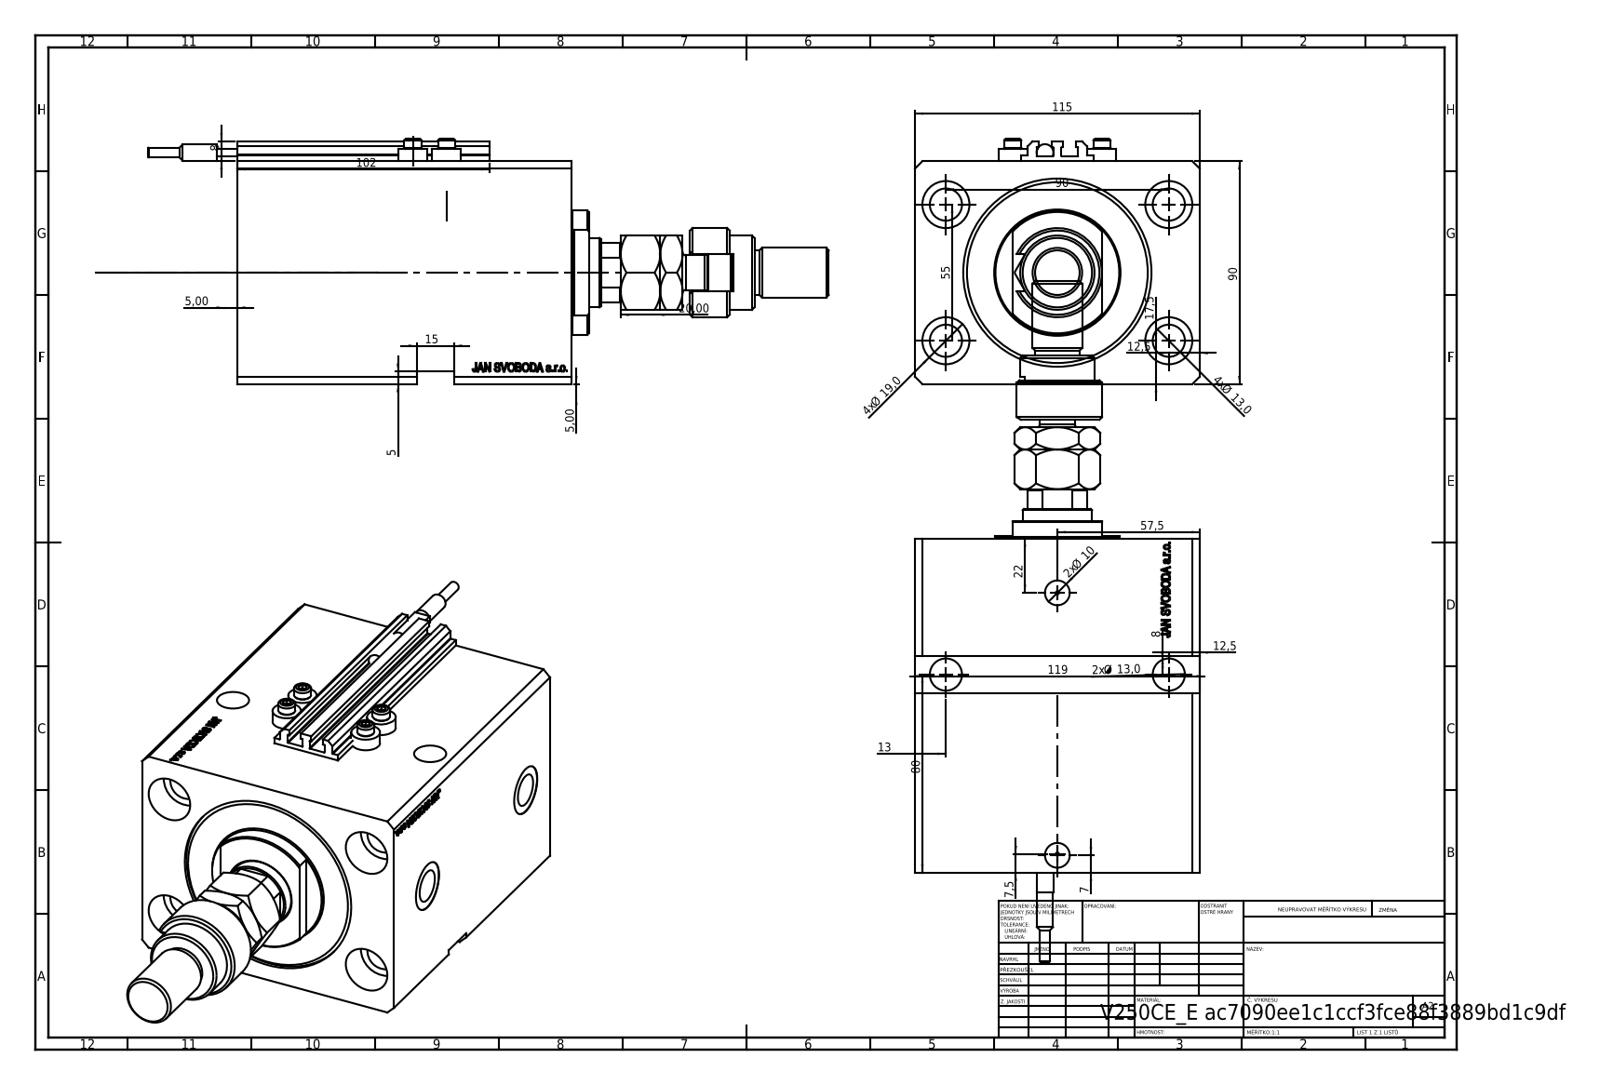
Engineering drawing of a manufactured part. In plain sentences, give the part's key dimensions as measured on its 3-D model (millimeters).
The part is named "FEMALE_PART_FOR_DFA; V250CE_C_VCP; V250CE_VC_E; SWITCH_V250CE (+3 more)". Its 3-D file was written by "SolidWorks 2019 (CONFIG_CONTROL_DESIGN)". It is 11 solids with 1218 faces: 587 planar, 145 cylindrical and 486 other. Overall it measures 274.9 by 115 by 99 millimeters. Its volume is 1 228 000 cubic millimeters and its surface area 199 699 square millimeters. Round holes: 6 of diameter 13, 4 of diameter 1.25, 4 of diameter 4, 4 of diameter 19, 2 of diameter 10, 2 of diameter 13.16, 2 of diameter 20, 1 of diameter 18.5, 1 of diameter 28, 1 of diameter 63, 1 of diameter 76. Round bosses or shafts: 4 of diameter 11.6, 4 of diameter 7, 1 of diameter 50, 1 of diameter 36, 1 of diameter 30, 1 of diameter 22, 1 of diameter 20, 1 of diameter 18. Partial cylindrical surfaces (rounded edges, fillets, slot ends): 10 of radius 0.2, 1 of radius 7.5, 1 of radius 12, 1 of radius 13.5. The main face-to-face distances are 90, 115, 135, 87, 17.9, 117.1, 104.9, 30.1, 50, 54.9. The hole center spacings are 52.74, 90, 13.6, 27.39, 28.46, 33.62, 36, 38.48.
